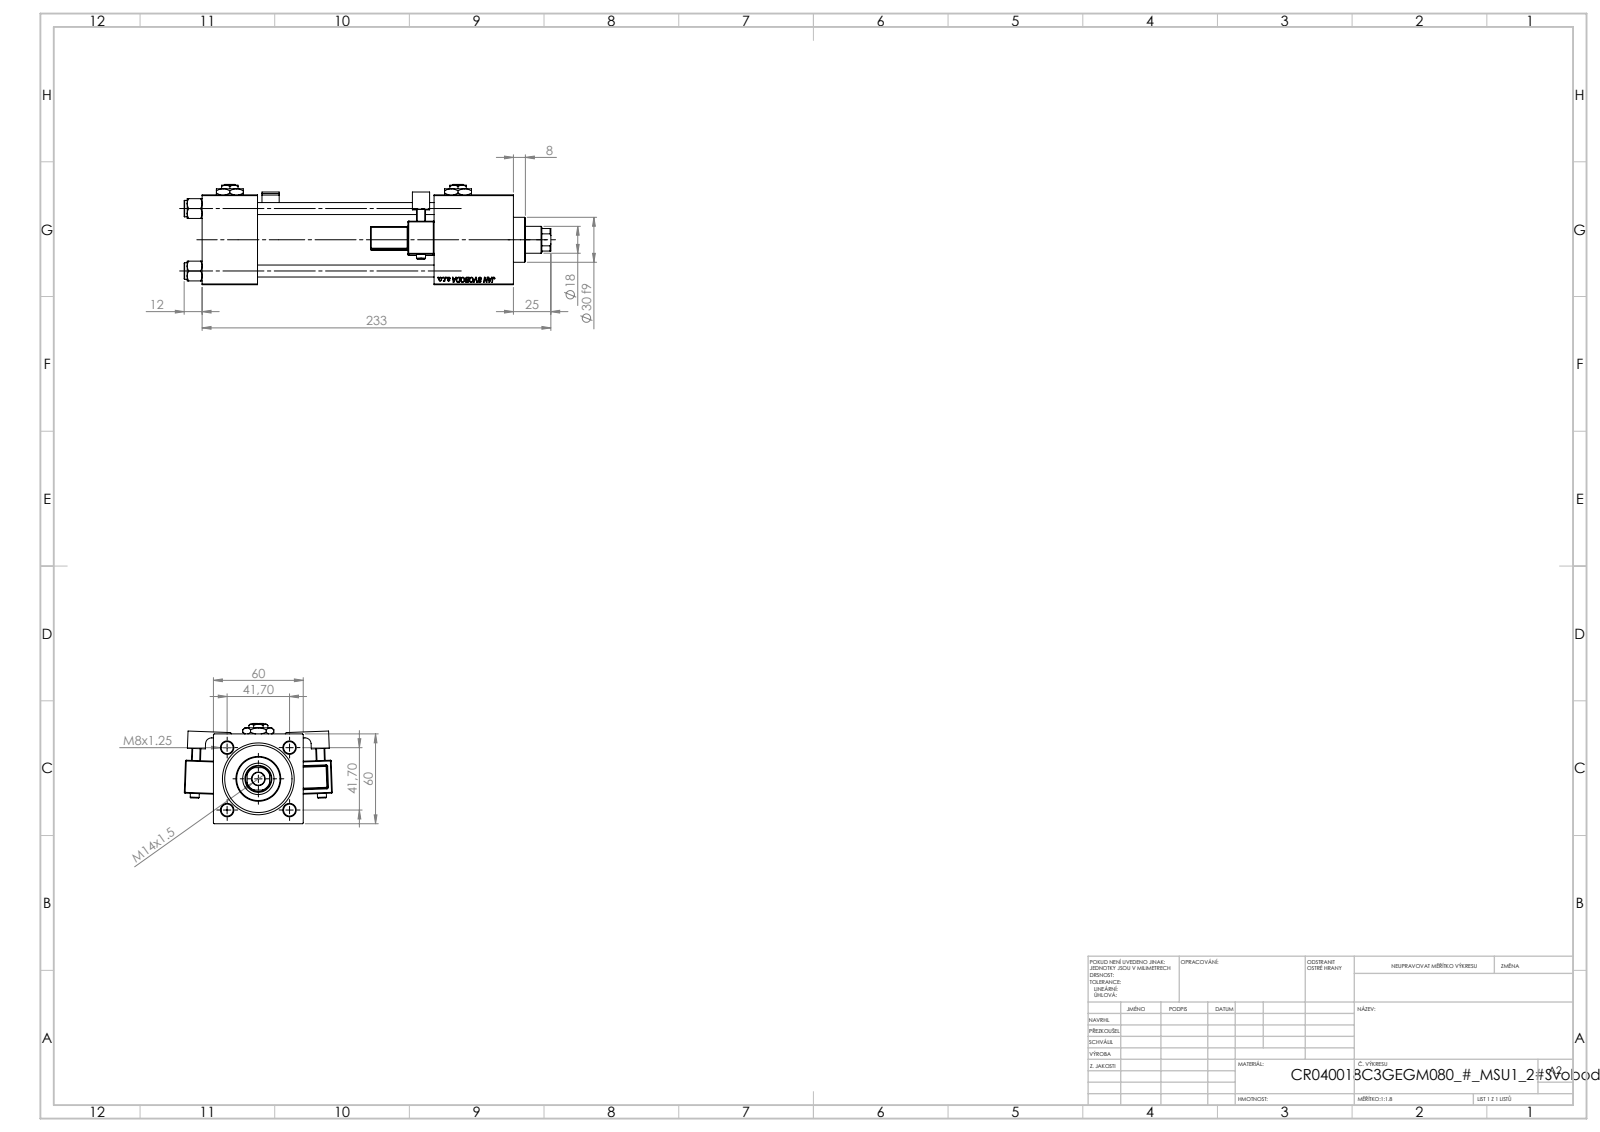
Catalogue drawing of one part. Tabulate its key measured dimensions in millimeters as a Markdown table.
| quantity | value |
| --- | --- |
| part name | Zatka_pro_OIL_PORT; NUT_M5_C; V215CR_C_Body; V215CR_C_TYCINKA (+3 more) |
| STEP written by | SolidWorks 2019 (CONFIG_CONTROL_DESIGN) |
| units | millimeters |
| bodies | 15 solids, 1404 faces (632 planar, 158 cylindrical, 614 other) |
| overall size | 245 × 98.85 × 67 |
| volume | 491 325 mm³ |
| surface area | 146 058 mm² |
| round holes (diameter × count) | 8 × 4, 7 × 2, 16.66 × 2, 24 × 2, 8.5 × 1, 18 × 1, 21 × 1, 31 × 1, 40 × 1, 45 × 1 |
| round bosses / shafts (diameter × count) | 11 × 4, 6 × 2, 46 × 1, 30 × 1 |
| partial cylindrical surfaces (radius × count) | 0.5 × 48, 1 × 2, 2.5 × 2, 4 × 2, 8.5 × 1 |
| main face-to-face distances | 60, 37, 155, 118, 53, 208, 171, 179.3, 142.3, 24.3 |
| hole center spacings | 29.49, 41.7, 58.97, 152.5 |
